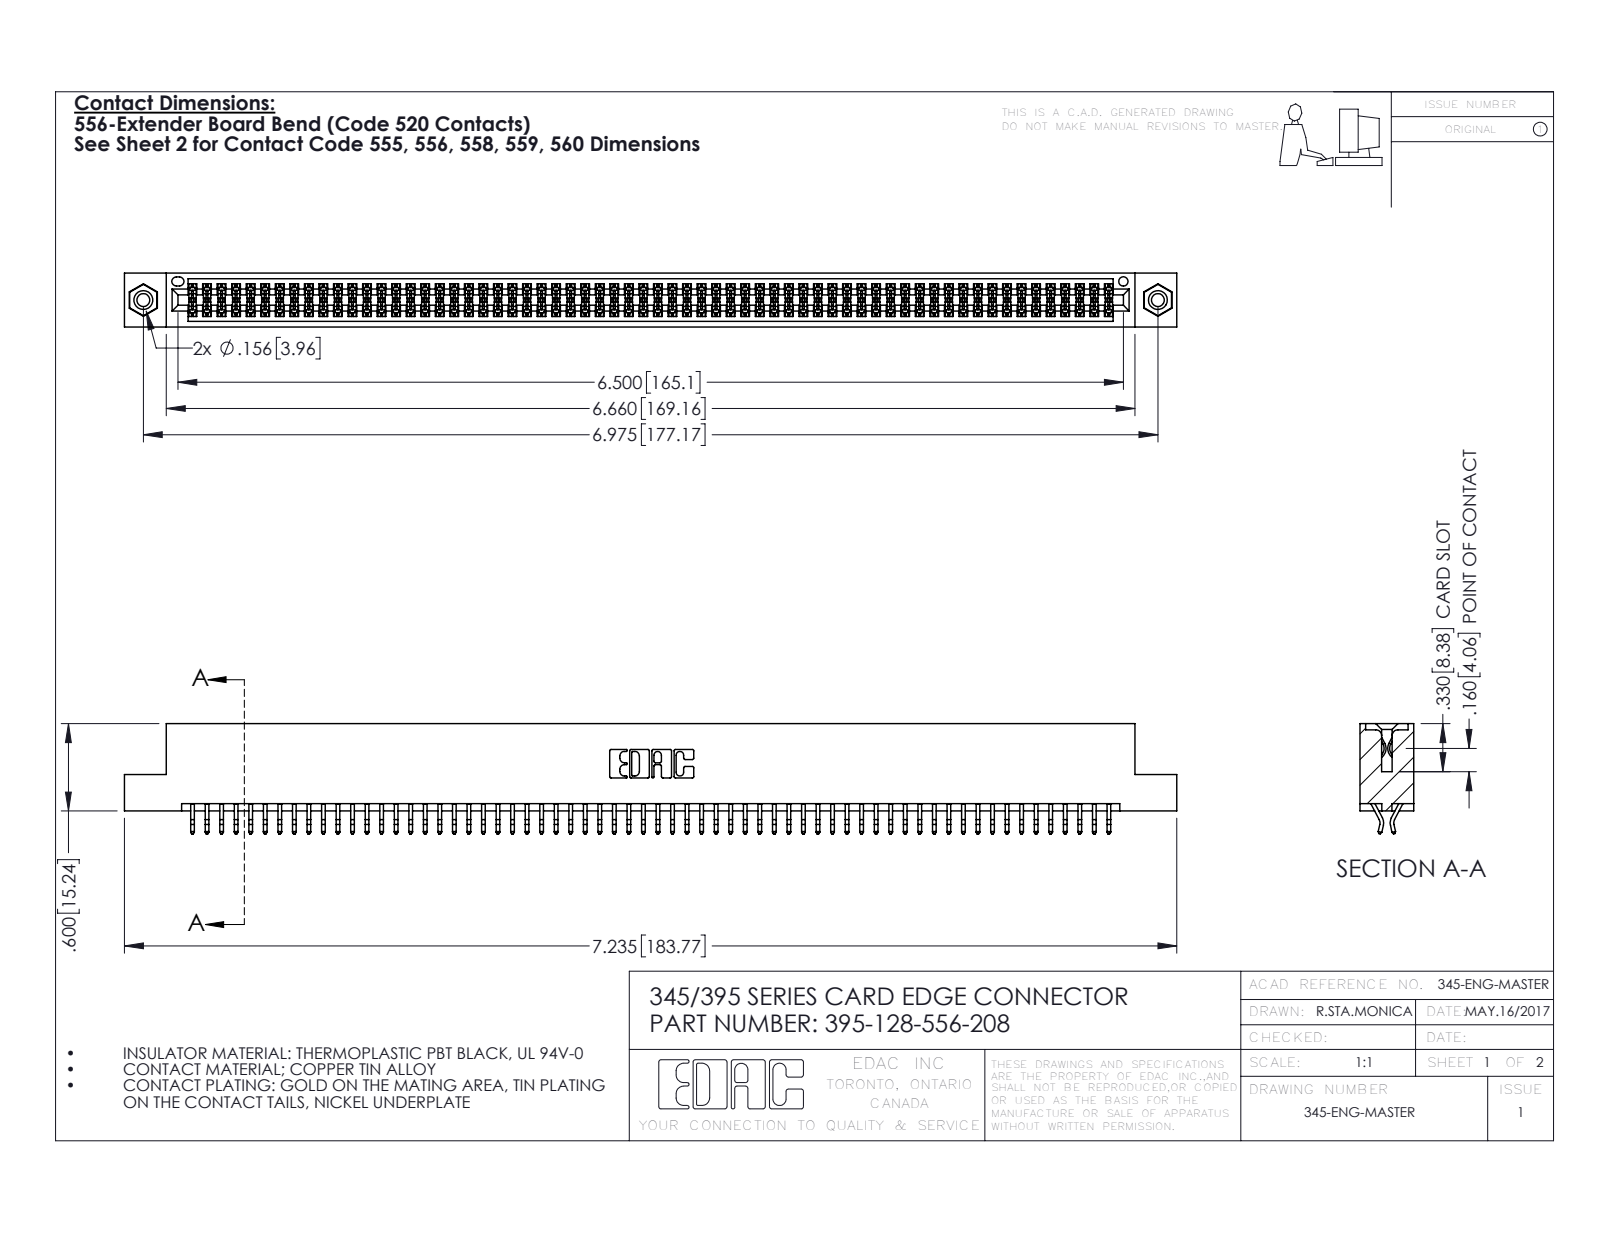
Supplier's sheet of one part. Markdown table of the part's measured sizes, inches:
| quantity | value |
| --- | --- |
| part name | 345-250-001_345-250-003-102; 345-292-001_556 Tail; 395-128-556-208; 345 Part_Flush Mounting Lugs - 0.156 Dia-TI |
| STEP written by | SolidWorks 2016 (CONFIG_CONTROL_DESIGN) |
| units | inches |
| bodies | 131 solids, 7354 faces (4848 planar, 2490 cylindrical, 16 other) |
| overall size | 7.235 × 0.757 × 0.37 |
| volume | 1.101 in³ |
| surface area | 41.85 in² |
| round holes (diameter × count) | 0.089 × 2, 0.125 × 2, 0.156 × 2, 0.064 × 1 |
| round bosses / shafts (diameter × count) | 0.155 × 2 |
| partial cylindrical surfaces (radius × count) | 0.006 × 192, 0.01 × 22, 0.007 × 6, 0.031 × 6, 0.026 × 3, 0.01 × 2, 0.014 × 2, 0.019 × 2 |
| main face-to-face distances | 0.072, 0.298, 0.37, 0.2, 0.025, 0.098, 0.272, 0.225, 0.175, 0.149 |
| hole center spacings | 0.27, 6.739, 6.975 |
